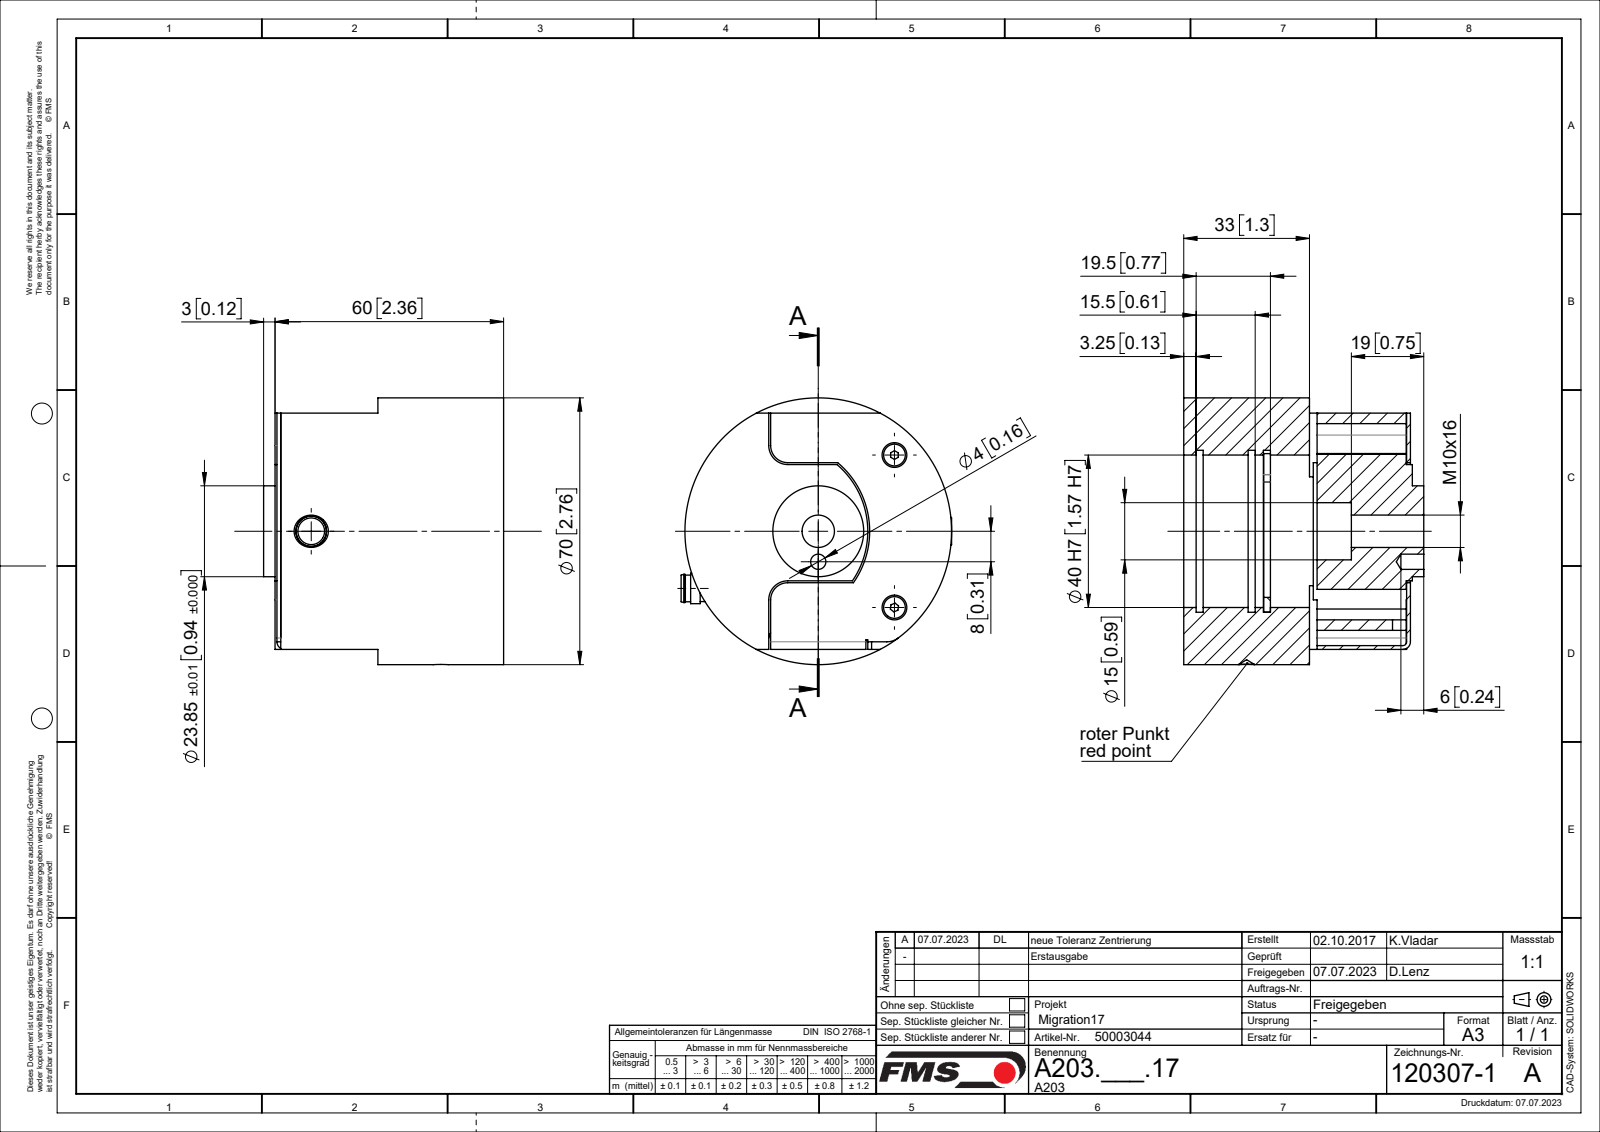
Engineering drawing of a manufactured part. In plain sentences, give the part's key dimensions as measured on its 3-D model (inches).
The part is named "Flanschstecker_M8-4pol; 120307.1_stp; 111107-3_01; Se-Schr DIN7991_M3x8 (+3 more)". Its 3-D file was written by "SolidWorks 2018 (CONFIG_CONTROL_DESIGN)". It is 7 solids with 237 faces: 82 planar, 105 cylindrical and 50 other. Overall it measures 2.795 by 2.756 by 2.48 inches. Its volume is 10.52 cubic inches and its surface area 60.84 square inches. Round holes: 4 of diameter 0.098, 2 of diameter 0.157, 1 of diameter 0.197, 1 of diameter 0.224, 1 of diameter 0.228, 1 of diameter 0.307, 1 of diameter 0.315, 1 of diameter 0.335, 1 of diameter 0.591, 1 of diameter 1.575, 1 of diameter 1.673. Round bosses or shafts: 4 of diameter 0.039, 2 of diameter 0.224, 2 of diameter 0.118, 1 of diameter 2.756, 1 of diameter 0.939, 1 of diameter 0.315, 1 of diameter 0.295, 1 of diameter 0.291. Partial cylindrical surfaces (rounded edges, fillets, slot ends): 4 of radius 0.004, 3 of radius 0.079, 3 of radius 0.197, 2 of radius 0.147, 2 of radius 0.177, 1 of radius 0.039, 1 of radius 0.394, 1 of radius 0.608. The main face-to-face distances are 0.039, 2.303, 0.925, 1.378, 1.004, 0.965, 1.043, 0.079, 1.299, 2.343. The hole center spacings are 0.698, 0.994, 1.113, 0.315, 0.526, 0.565, 0.602, 0.918.
